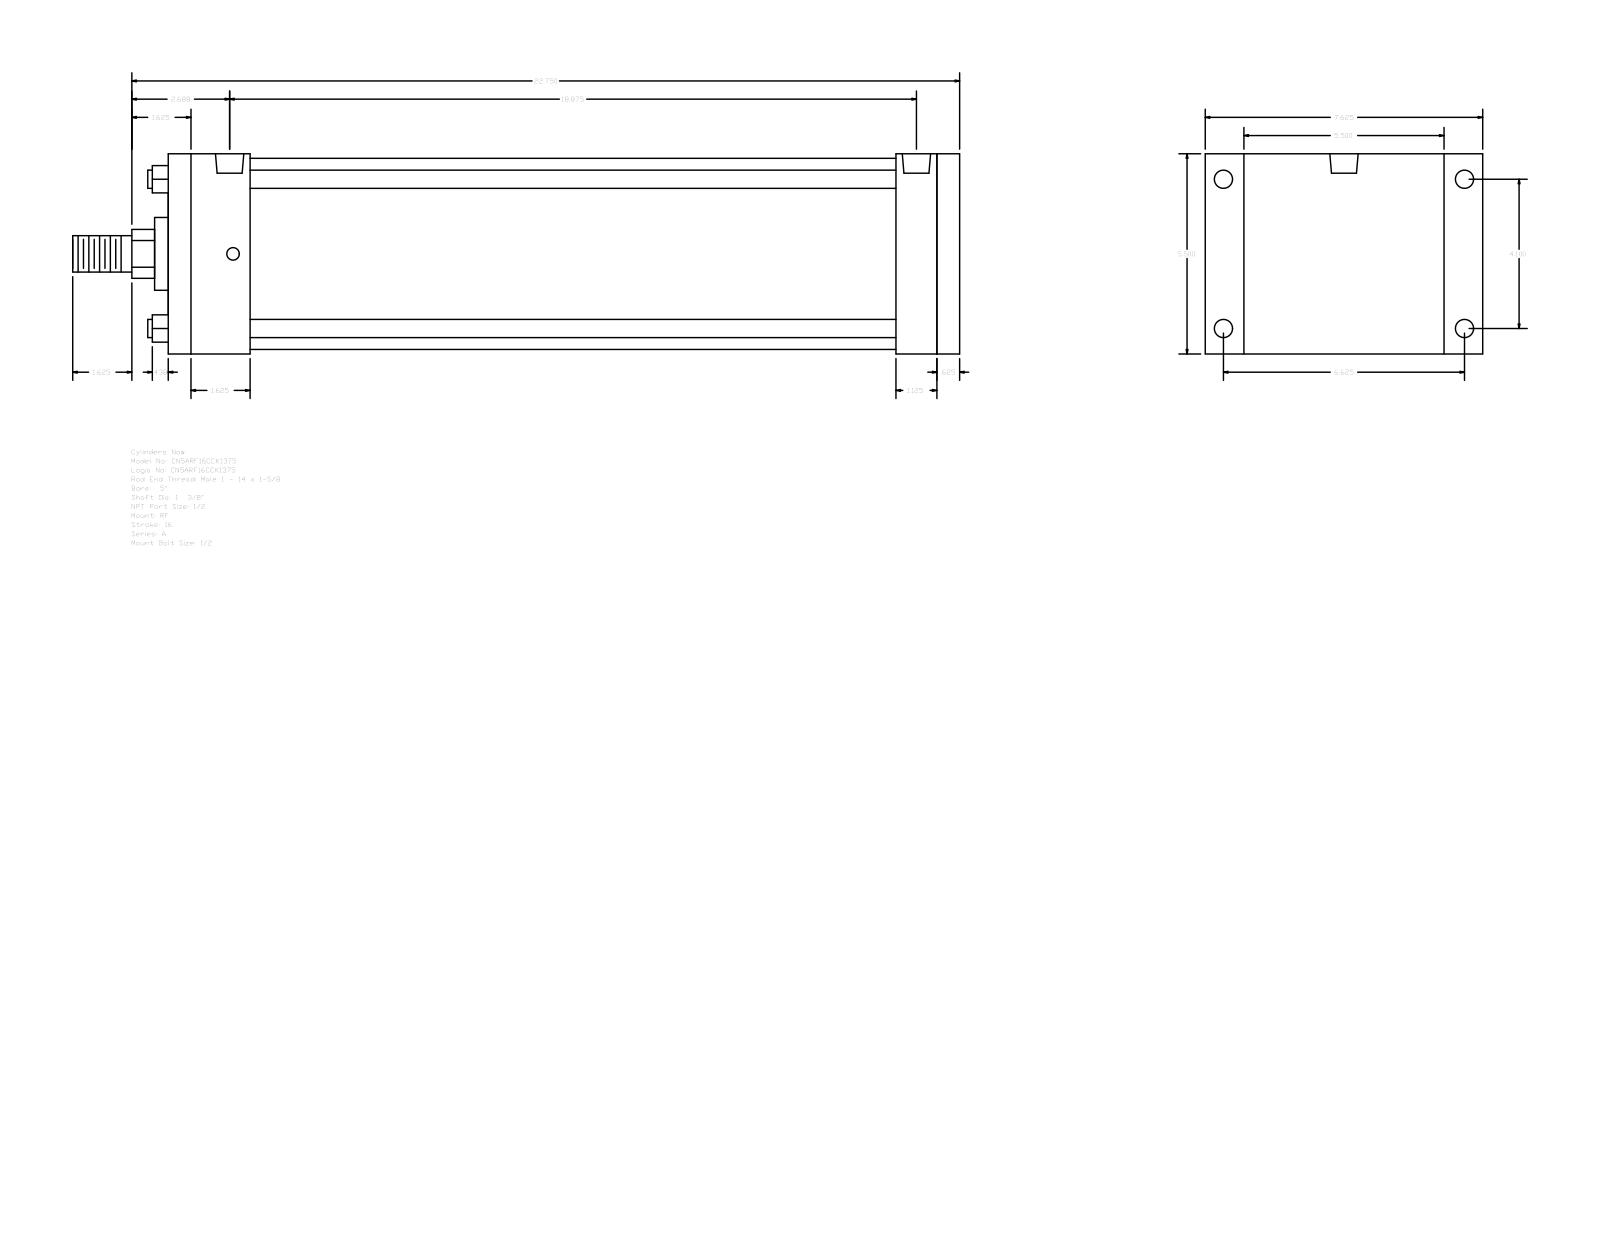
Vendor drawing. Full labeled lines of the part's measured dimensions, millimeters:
Part name (STEP PRODUCT): A_RF__0500_1.375
STEP written by: GSSL Pune (CONFIG_CONTROL_DESIGN)
Units: millimetres
Bodies: 0 solids, 92 faces (64 planar, 28 cylindrical, 0 other)
Overall size (bounding box): 619.12 × 193.68 × 139.7
Round holes (diameter × count): ⌀8.73 ×4, ⌀12.7 ×4, ⌀19.77 ×2
Round bosses / shafts (diameter × count): ⌀12.7 ×4, ⌀133.35 ×1, ⌀50.8 ×1, ⌀34.92 ×1, ⌀25.4 ×1
Partial cylindrical surfaces — rounded edges, fillets, slot ends (radius × count): R17.06 ×1
Main face-to-face distances: 139.7, 552.45, 536.58, 15.87, 57.15, 28.58, 479.43, 495.3, 508, 450.85
Hole centre spacings: 2.39, 104.14, 168.28, 197.9, 474.65, 477.04, 479.43
